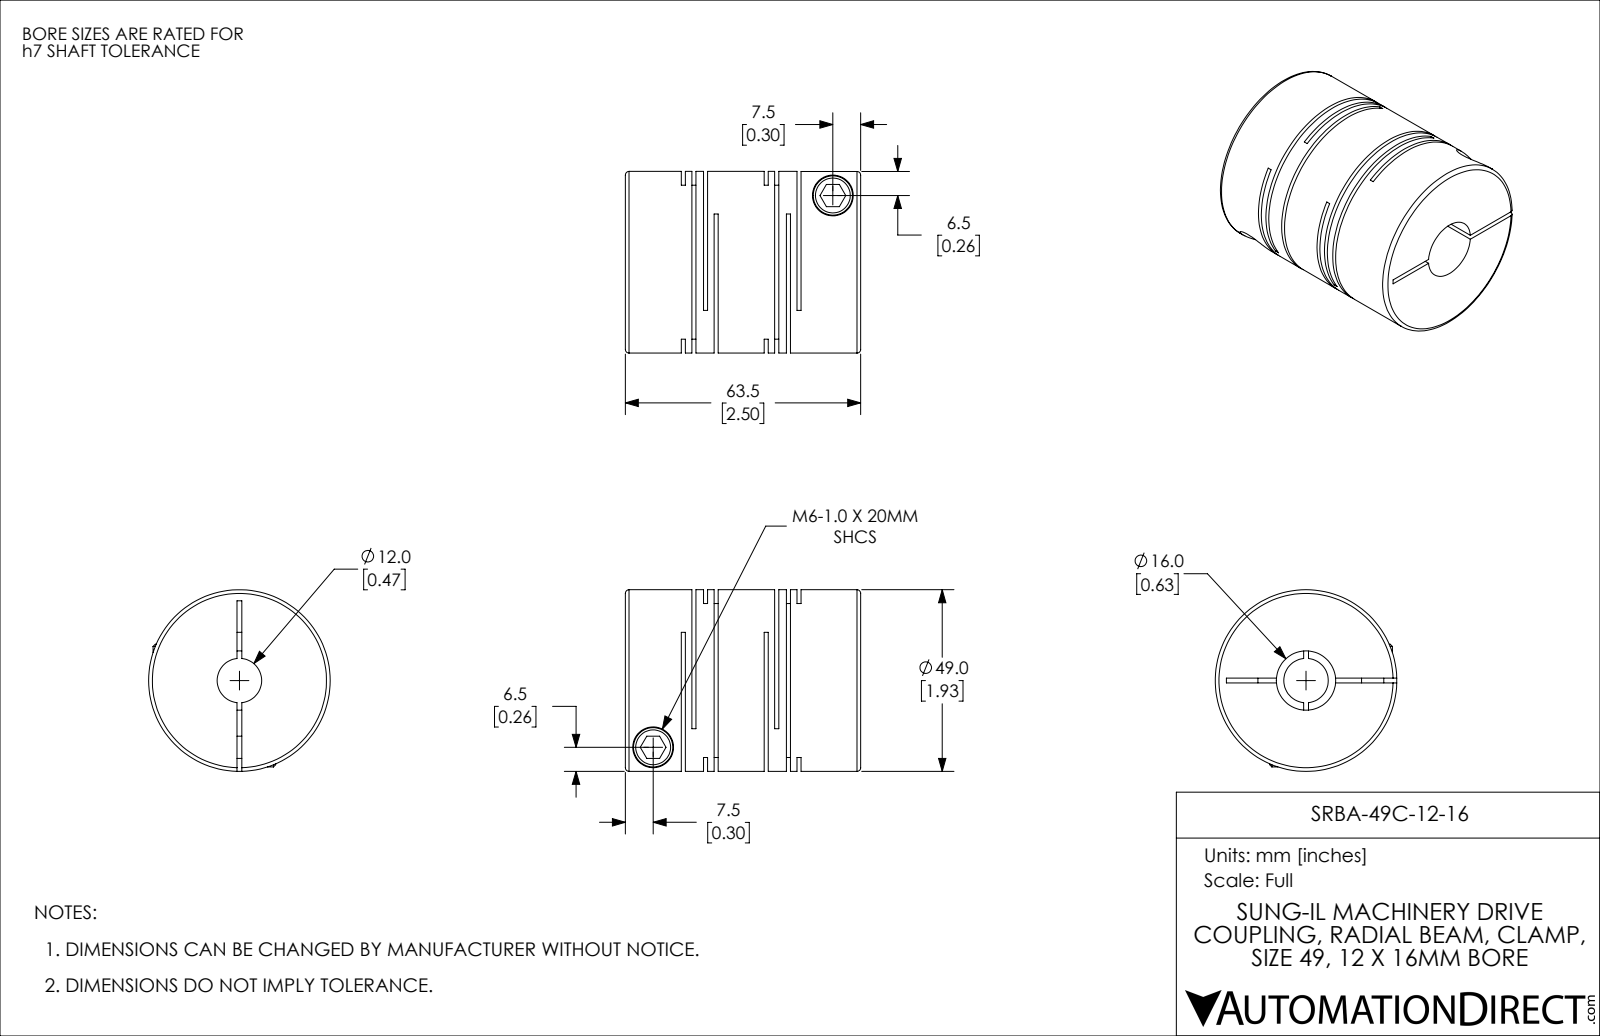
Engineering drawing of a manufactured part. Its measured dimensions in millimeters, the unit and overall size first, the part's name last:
Units: millimetres
Overall size (bounding box): 63.5 × 49 × 49
Round holes (diameter × count): ⌀6 ×2, ⌀11 ×2, ⌀12 ×1, ⌀16 ×1
Round bosses / shafts (diameter × count): ⌀10.6 ×2, ⌀49 ×1
Main face-to-face distances: 6, 1.1, 2.85, 22.35, 1.75, 4.9, 21.25, 3.15, 19.5, 16.35
Volume: 93 503 mm³ · Surface area: 39 643 mm²
Bodies: 1 solid, 114 faces (60 planar, 42 cylindrical, 12 other)
Part name (STEP PRODUCT): SRBA-49C-12-16
STEP written by: SolidWorks 2021 (CONFIG_CONTROL_DESIGN)
